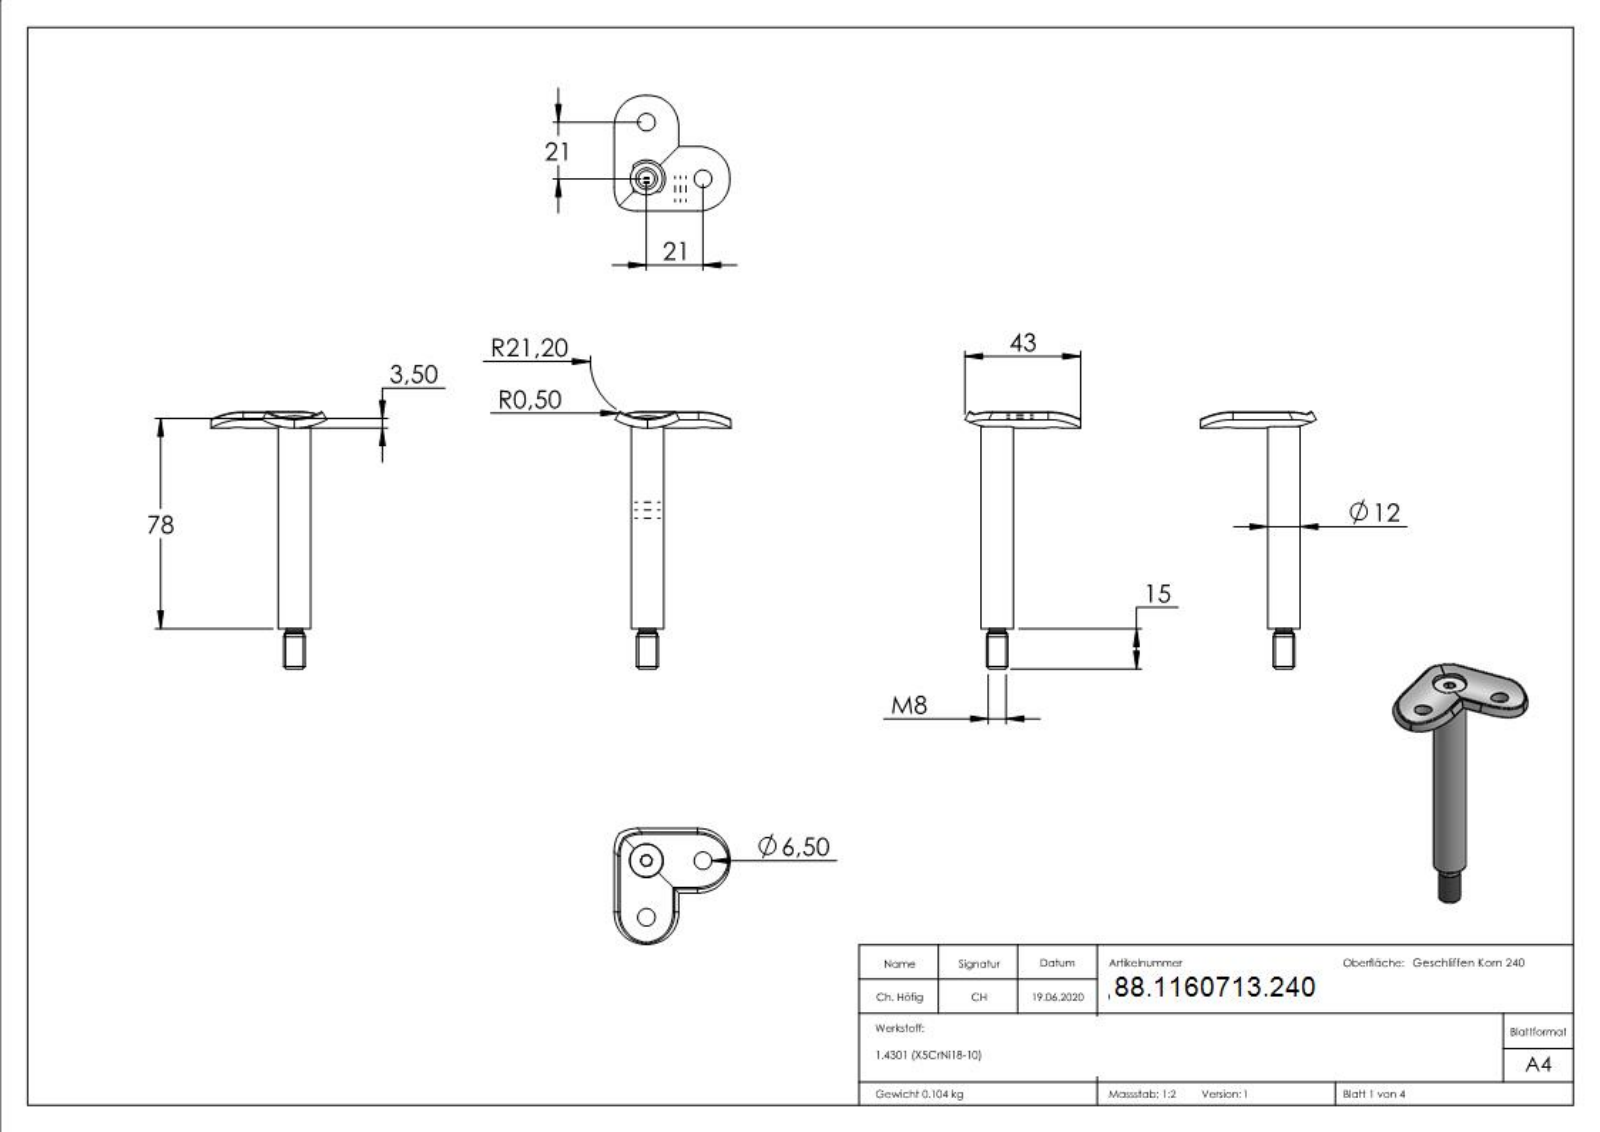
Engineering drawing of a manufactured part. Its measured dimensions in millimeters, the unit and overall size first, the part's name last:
Units: millimetres
Overall size (bounding box): 95.5 × 43 × 43
Round holes (diameter × count): ⌀6.5 ×2, ⌀5 ×1, ⌀8.5 ×1, ⌀12.5 ×1
Round bosses / shafts (diameter × count): ⌀12 ×1, ⌀8 ×1, ⌀6 ×1
Partial cylindrical surfaces — rounded edges, fillets, slot ends (radius × count): R0.5 ×4, R12 ×4, R21.2 ×2, R24.7 ×2, R7 ×1, R10 ×1
Main face-to-face distances: 2.55, 90, 92.55, 4, 80.55, 9.45, 12, 0.45, 89.55, 9
Hole centre spacings: 21, 29.7
Volume: 13 127 mm³ · Surface area: 7 293 mm²
Bodies: 3 solids, 297 faces (138 planar, 35 cylindrical, 124 other)
Part name (STEP PRODUCT): DIN-7991_-_DIN7991 M6x16_DIN7991 M6x12; 50236-Konfig_50236-240-75-M6; 60713-240; 60179-240_60179-240
STEP written by: SolidWorks 2015 (CONFIG_CONTROL_DESIGN)
